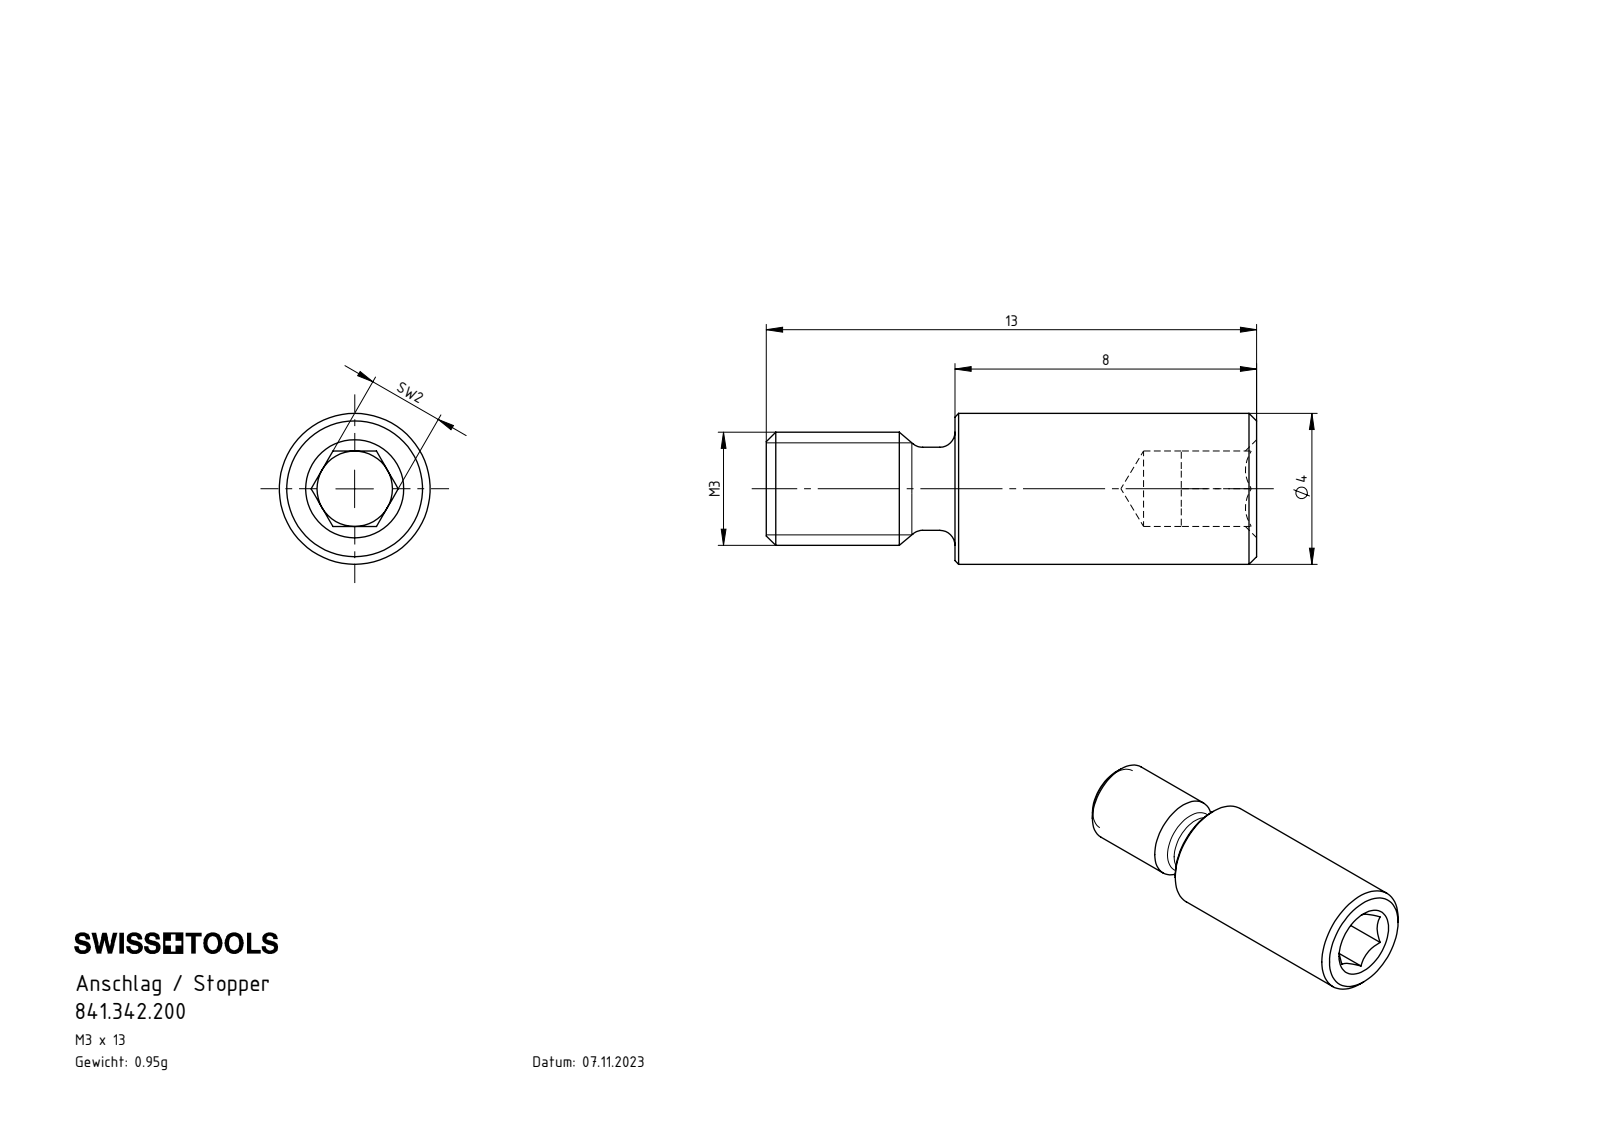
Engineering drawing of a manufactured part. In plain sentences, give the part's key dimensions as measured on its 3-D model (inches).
The part is named "841.342.200". Its 3-D file was written by "SolidWorks 2022 (AUTOMOTIVE_DESIGN)". It is 1 solid with 39 faces: 15 planar, 8 cylindrical and 16 other. Overall it measures 0.512 by 0.157 by 0.157 inches. Its volume is 0.007 cubic inches and its surface area 0.293 square inches. Round holes: 1 of diameter 0.079. Round bosses or shafts: 1 of diameter 0.157, 1 of diameter 0.118, 1 of diameter 0.087. The main face-to-face distances are 0.079, 0.512, 0.197, 0.315, 0.433, 0.236.
